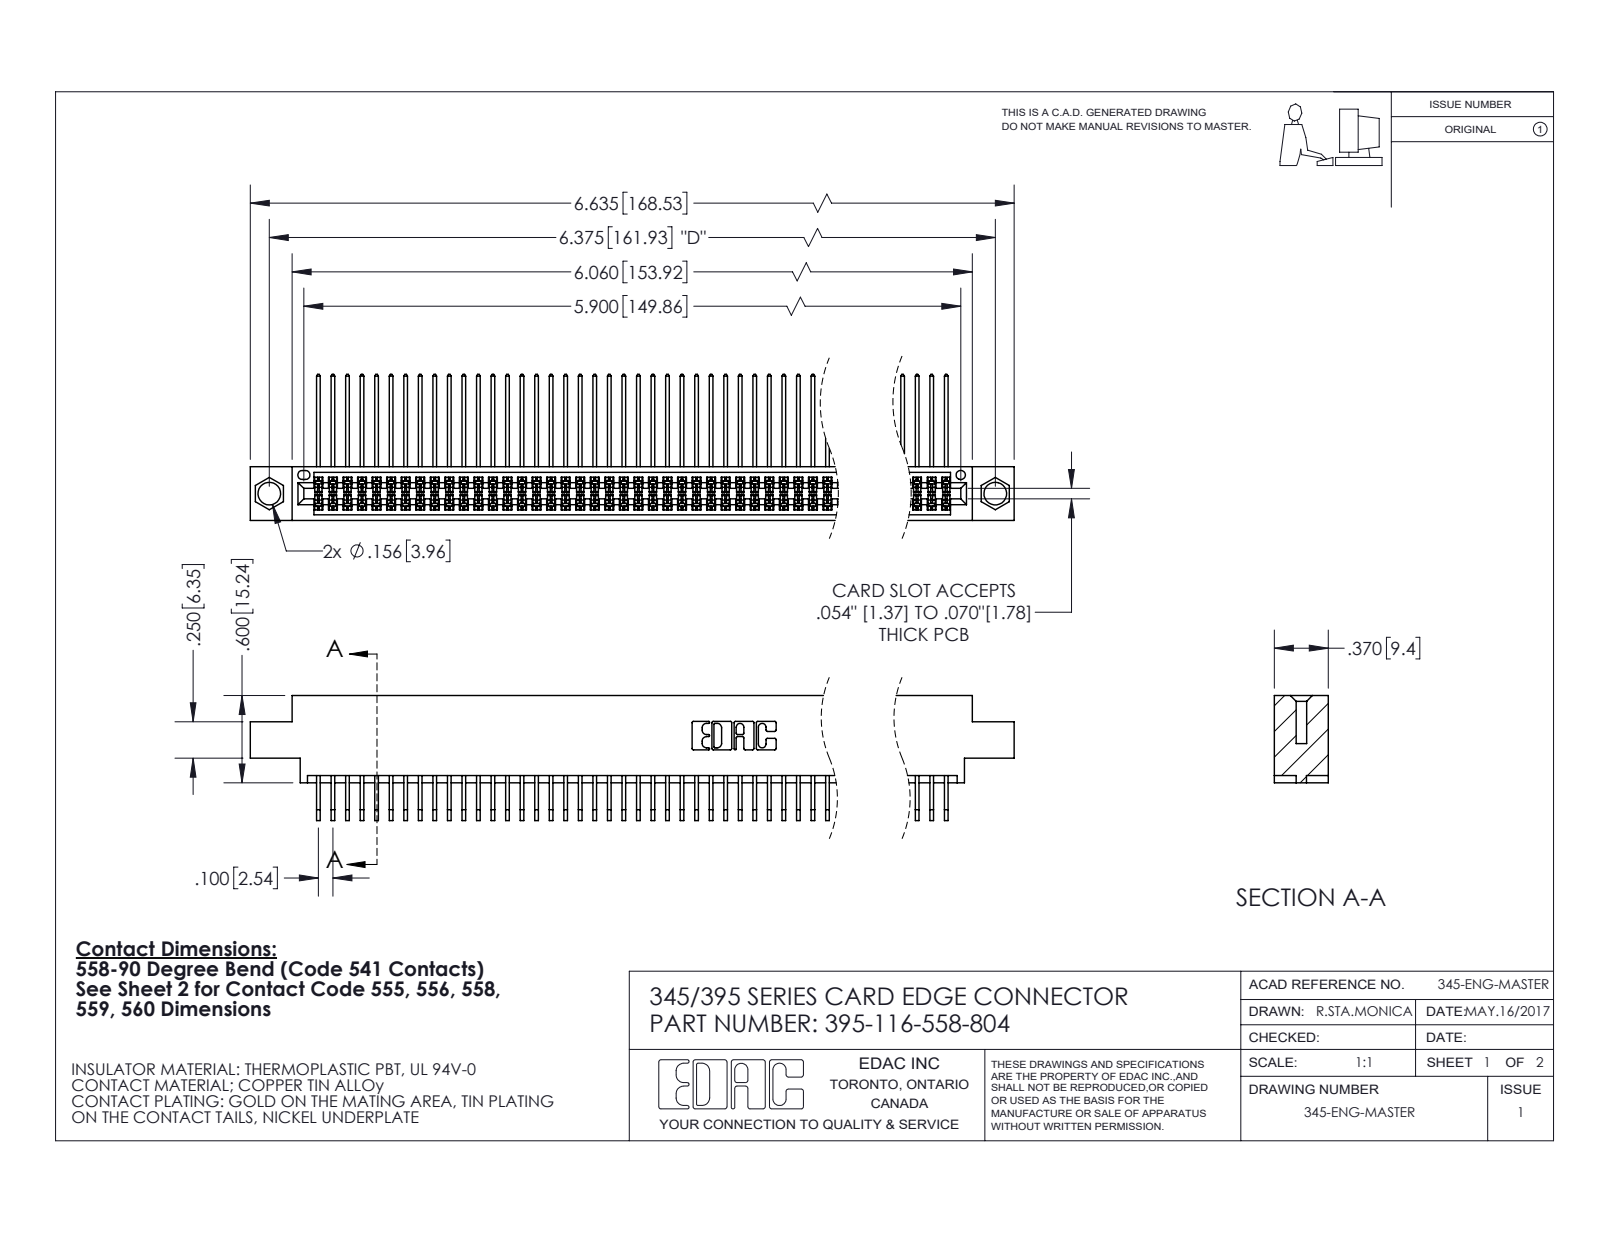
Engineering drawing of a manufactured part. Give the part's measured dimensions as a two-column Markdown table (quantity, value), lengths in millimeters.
| quantity | value |
| --- | --- |
| part name | 345-292-001_558 Tail - 2; 345 Part_0.170 Offset - 0.156 Dia-TI; 395-116-558-804; 345-292-001_558 559 Tail - 1 |
| STEP written by | SolidWorks 2020 (CONFIG_CONTROL_DESIGN) |
| units | millimeters |
| bodies | 117 solids, 6176 faces (4158 planar, 2018 cylindrical, 0 other) |
| overall size | 168.5 × 25.5 × 21.8 |
| volume | 16 980 mm³ |
| surface area | 28 540 mm² |
| round holes (diameter × count) | 4 × 2, 1.6 × 1 |
| partial cylindrical surfaces (radius × count) | 0.2 × 174, 0.3 × 22, 0.2 × 6, 0.8 × 6, 0.7 × 3, 0.4 × 2, 0.5 × 2, 0.6 × 2 |
| main face-to-face distances | 1.8, 7.6, 5.1, 9.4, 2.5, 6.9, 0.6, 5.7, 4.4, 0.6 |
| hole center spacings | 6.9, 155.9, 161.9 |
